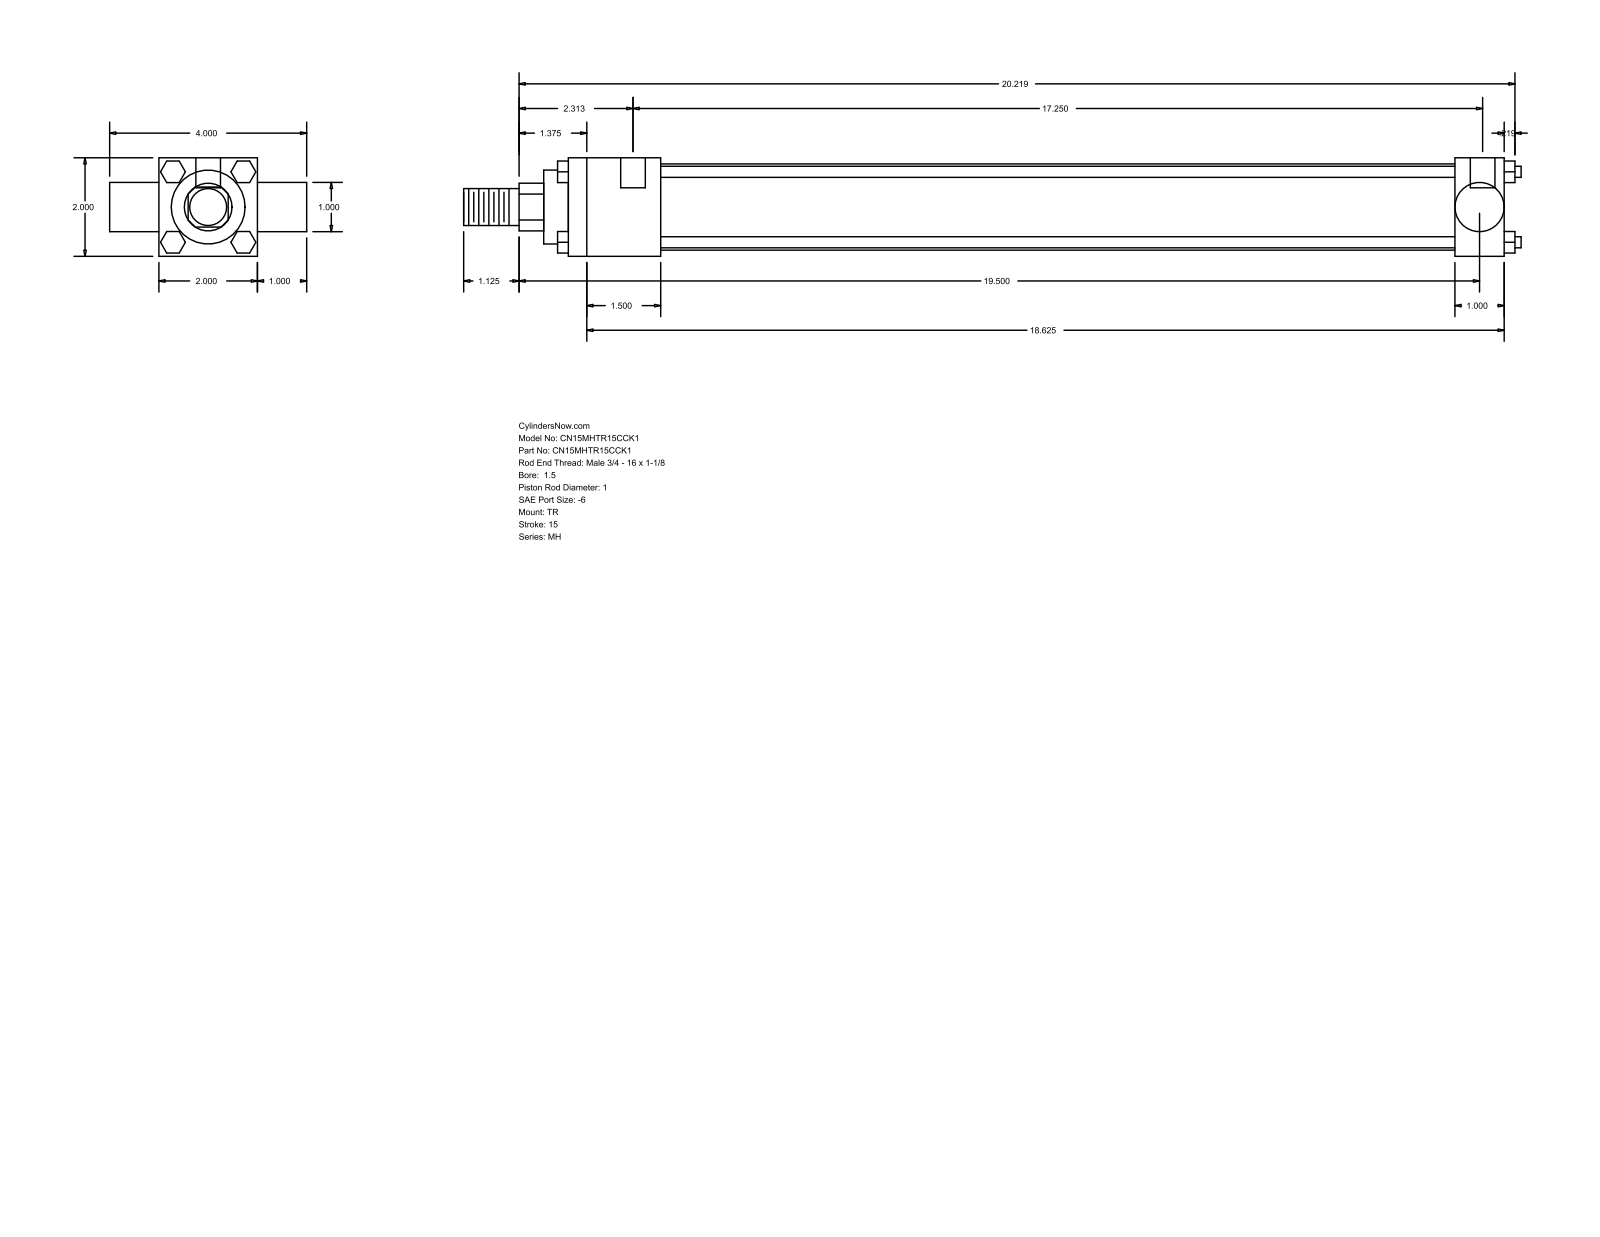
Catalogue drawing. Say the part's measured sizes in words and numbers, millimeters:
The part is named "MH_TR__0150_1". Its 3-D file was written by "GSSL Pune (CONFIG_CONTROL_DESIGN)". It is 0 solids with 120 faces: 92 planar, 28 cylindrical and 0 other. Overall it measures 545.31 by 101.6 by 50.8 millimeters. Round holes: 3 of diameter 5.56, 2 of diameter 12.7. Round bosses or shafts: 4 of diameter 5.71, 1 of diameter 44.45, 1 of diameter 38.1, 1 of diameter 25.4, 1 of diameter 25.35, 1 of diameter 19.05. Partial cylindrical surfaces (rounded edges, fillets, slot ends): 1 of radius 12.29. The main face-to-face distances are 50.8, 25.4, 482.6, 76.2, 47.63, 434.97, 457.2, 409.57, 101.6, 12.7. The hole center spacings are 3.18, 438.15, 441.33.
